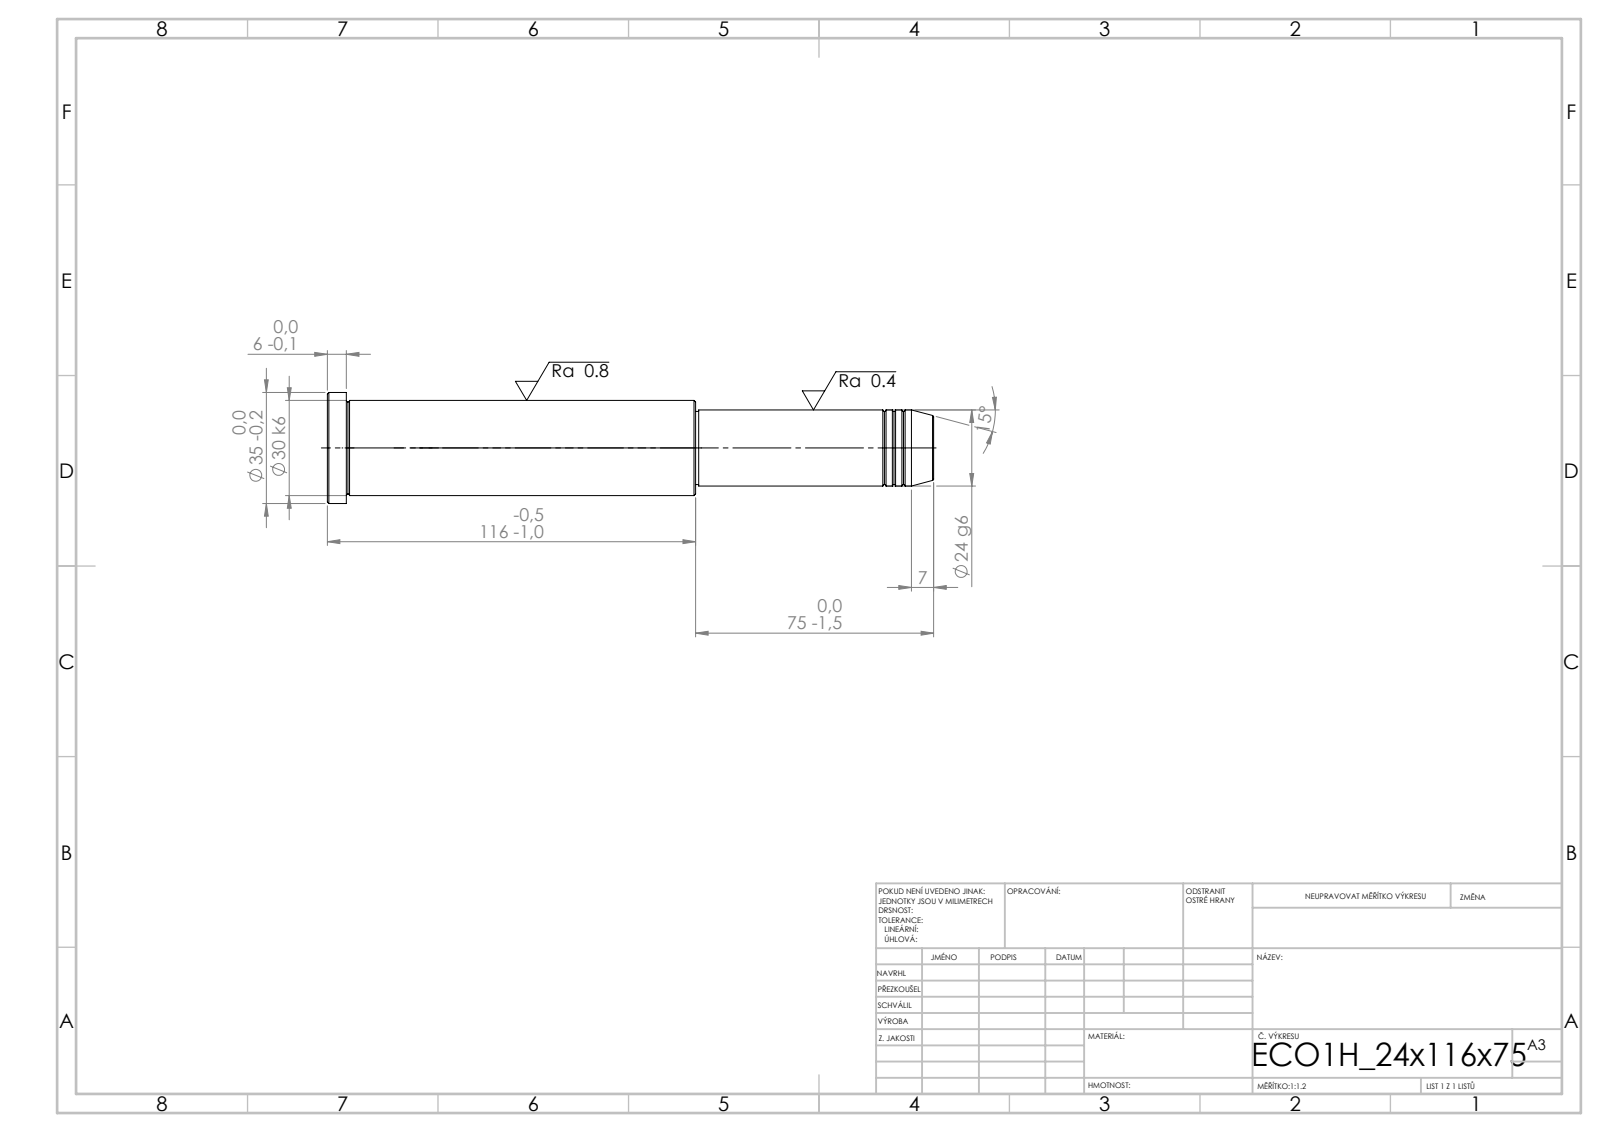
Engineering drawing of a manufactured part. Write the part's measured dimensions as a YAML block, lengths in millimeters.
step_written_by: "SolidWorks 2019 (CONFIG_CONTROL_DESIGN)"
units: millimeters
bodies: {solids: 1, faces: 43, planar: 5, cylindrical: 14, other: 24}
overall_size: [191, 35, 35]
volume: 116799
surface_area: 18625
round_bosses_or_shafts:
  - {diameter: 35, count: 1}
  - {diameter: 30, count: 1}
  - {diameter: 24, count: 1}
  - {diameter: 23, count: 1}
face_to_face_distances: [191, 185, 6, 75, 110, 116, 74, 1, 111, 117]
